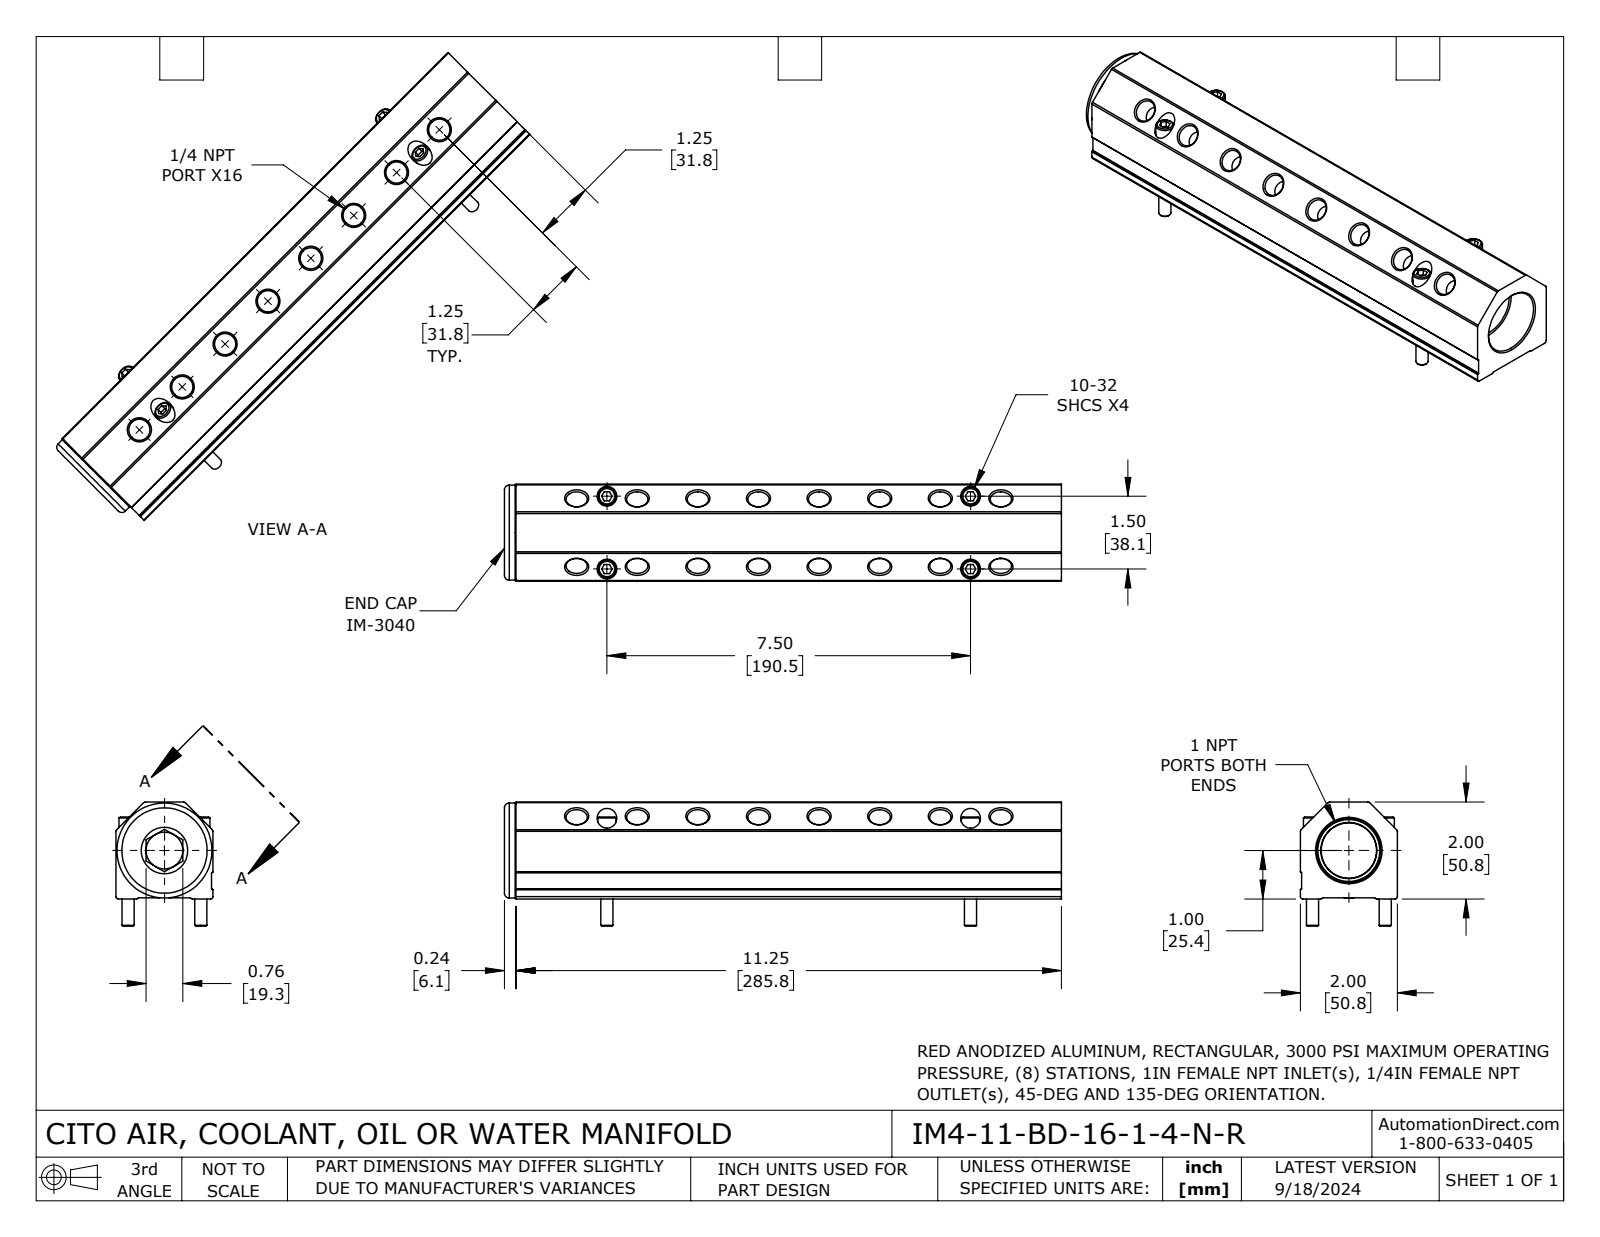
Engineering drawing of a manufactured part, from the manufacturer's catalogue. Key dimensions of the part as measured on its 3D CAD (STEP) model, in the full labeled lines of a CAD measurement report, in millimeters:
Part name (STEP PRODUCT): IM4-11-BD-16-1-4-N-R
STEP written by: SolidWorks 2023 (CONFIG_CONTROL_DESIGN)
Units: millimetres
Bodies: 6 solids, 245 faces (81 planar, 90 cylindrical, 74 other)
Overall size (bounding box): 291.8 × 65 × 50.8
Volume: 467 500 mm³ · Surface area: 102 500 mm²
Round holes (diameter × count): ⌀11.1 ×16, ⌀6.8 ×4, ⌀10.3 ×4, ⌀19.3 ×1, ⌀29.4 ×1, ⌀41.6 ×1
Round bosses / shafts (diameter × count): ⌀9.5 ×4, ⌀6.4 ×4, ⌀49.8 ×1, ⌀34.5 ×1, ⌀32.8 ×1, ⌀29 ×1
Partial cylindrical surfaces — rounded edges, fillets, slot ends (radius × count): R1.3 ×8, R0.3 ×4
Main face-to-face distances: 50.8, 50.2, 0.6, 0.7, 50.1, 285.8, 6.1, 291.8, 19.4, 13.3
Hole centre spacings: 31.8, 63.5, 95.3, 127, 158.8, 190.5, 38.1, 194.3
